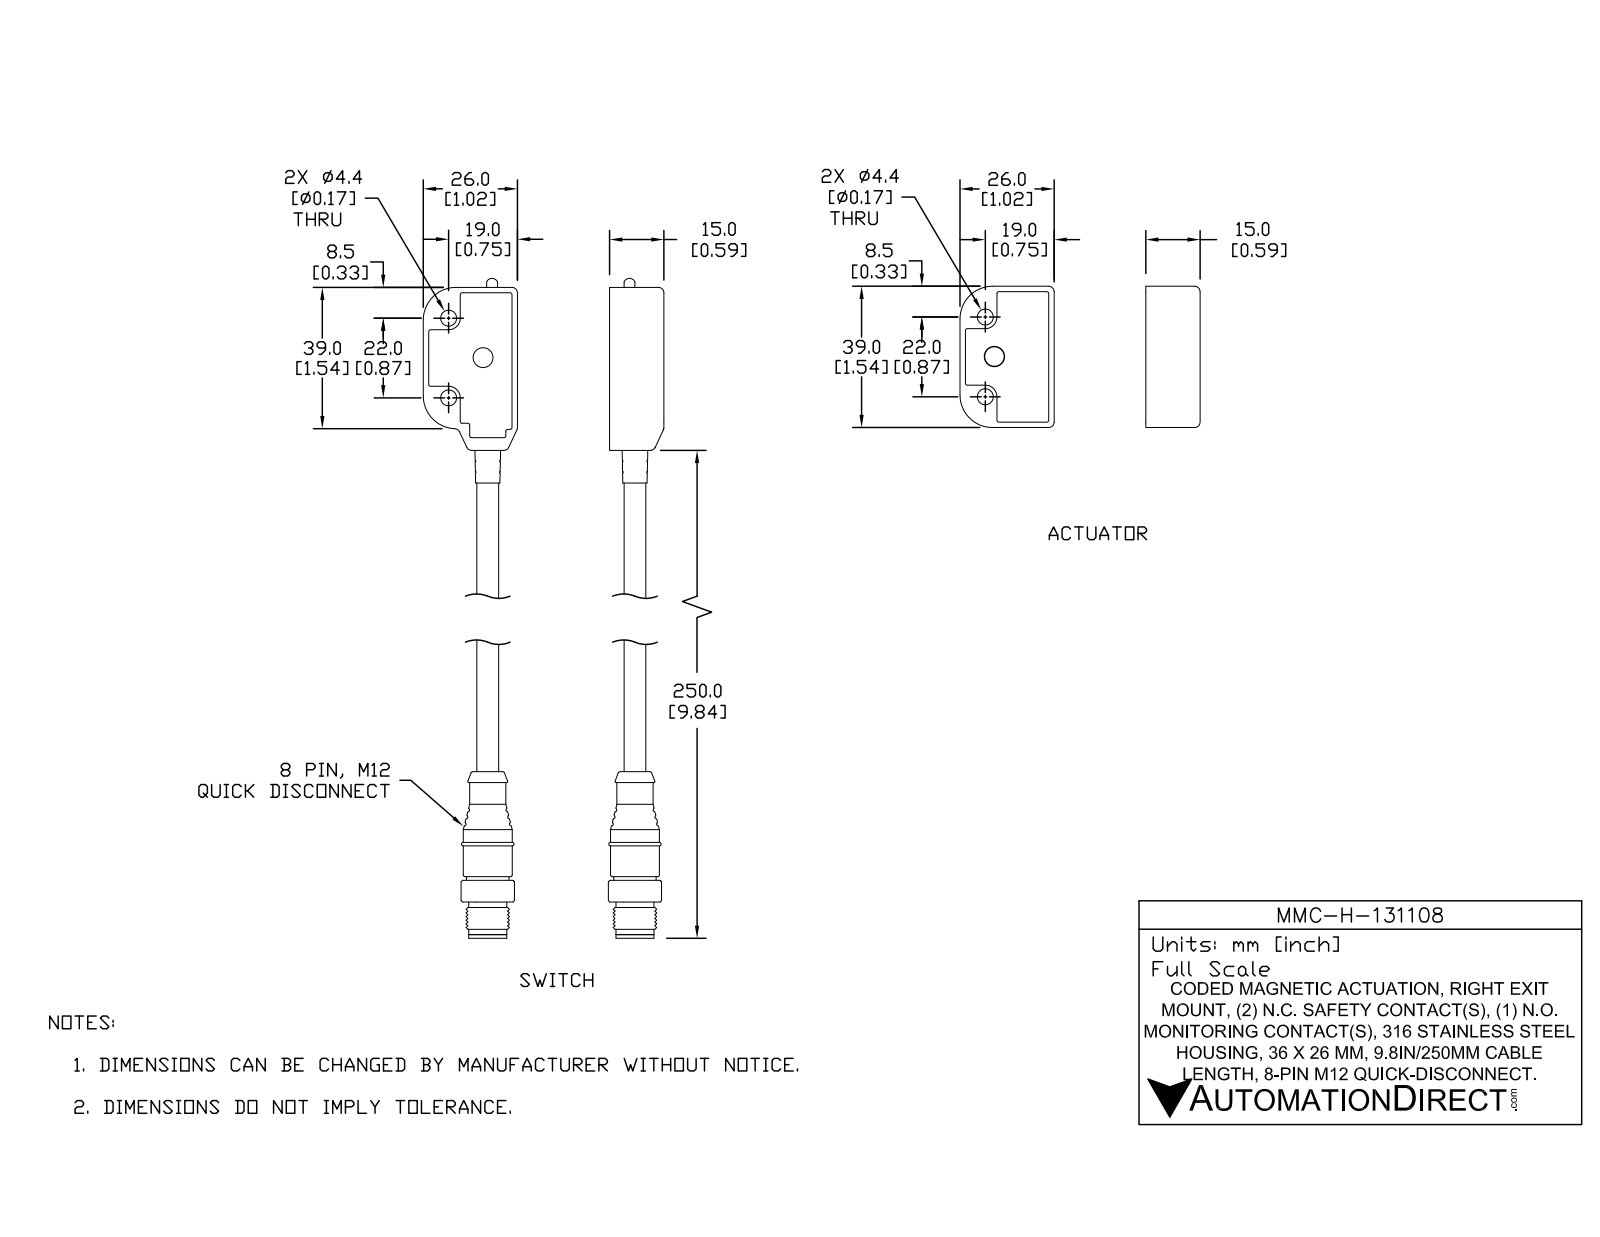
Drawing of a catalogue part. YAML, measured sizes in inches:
part_name: "MMC-H-131108; MMC-H-131108_2; MMC-H-131108_1"
step_written_by: "SolidWorks 2017 (AUTOMOTIVE_DESIGN)"
units: inches
bodies: {solids: 10, faces: 958, planar: 335, cylindrical: 344, other: 279}
overall_size: [11.713, 2.087, 0.604]
volume: 1.615
surface_area: 38.4
round_holes:
  - {diameter: 0.173, count: 4}
  - {diameter: 0.197, count: 2}
  - {diameter: 0.118, count: 1}
  - {diameter: 0.232, count: 1}
  - {diameter: 0.283, count: 1}
  - {diameter: 0.327, count: 1}
  - {diameter: 0.465, count: 1}
round_bosses_or_shafts:
  - {diameter: 0.031, count: 10}
  - {diameter: 0.079, count: 2}
  - {diameter: 0.531, count: 1}
  - {diameter: 0.461, count: 1}
  - {diameter: 0.413, count: 1}
  - {diameter: 0.394, count: 1}
  - {diameter: 0.374, count: 1}
  - {diameter: 0.339, count: 1}
partial_cylinders:
  - {radius: 0.02, count: 82}
  - {radius: 0.012, count: 26}
  - {radius: 0.059, count: 15}
  - {radius: 0.008, count: 8}
  - {radius: 0.157, count: 6}
  - {radius: 0.126, count: 4}
  - {radius: 0.13, count: 4}
  - {radius: 0.181, count: 4}
face_to_face_distances: [0.059, 0.575, 0.516, 0.098, 0.461, 0.52, 0.055, 0.591, 0.531, 0.965]
hole_center_spacings: [0.866, 1.535, 1.763, 0.076, 0.44, 0.448, 0.569, 0.575]
